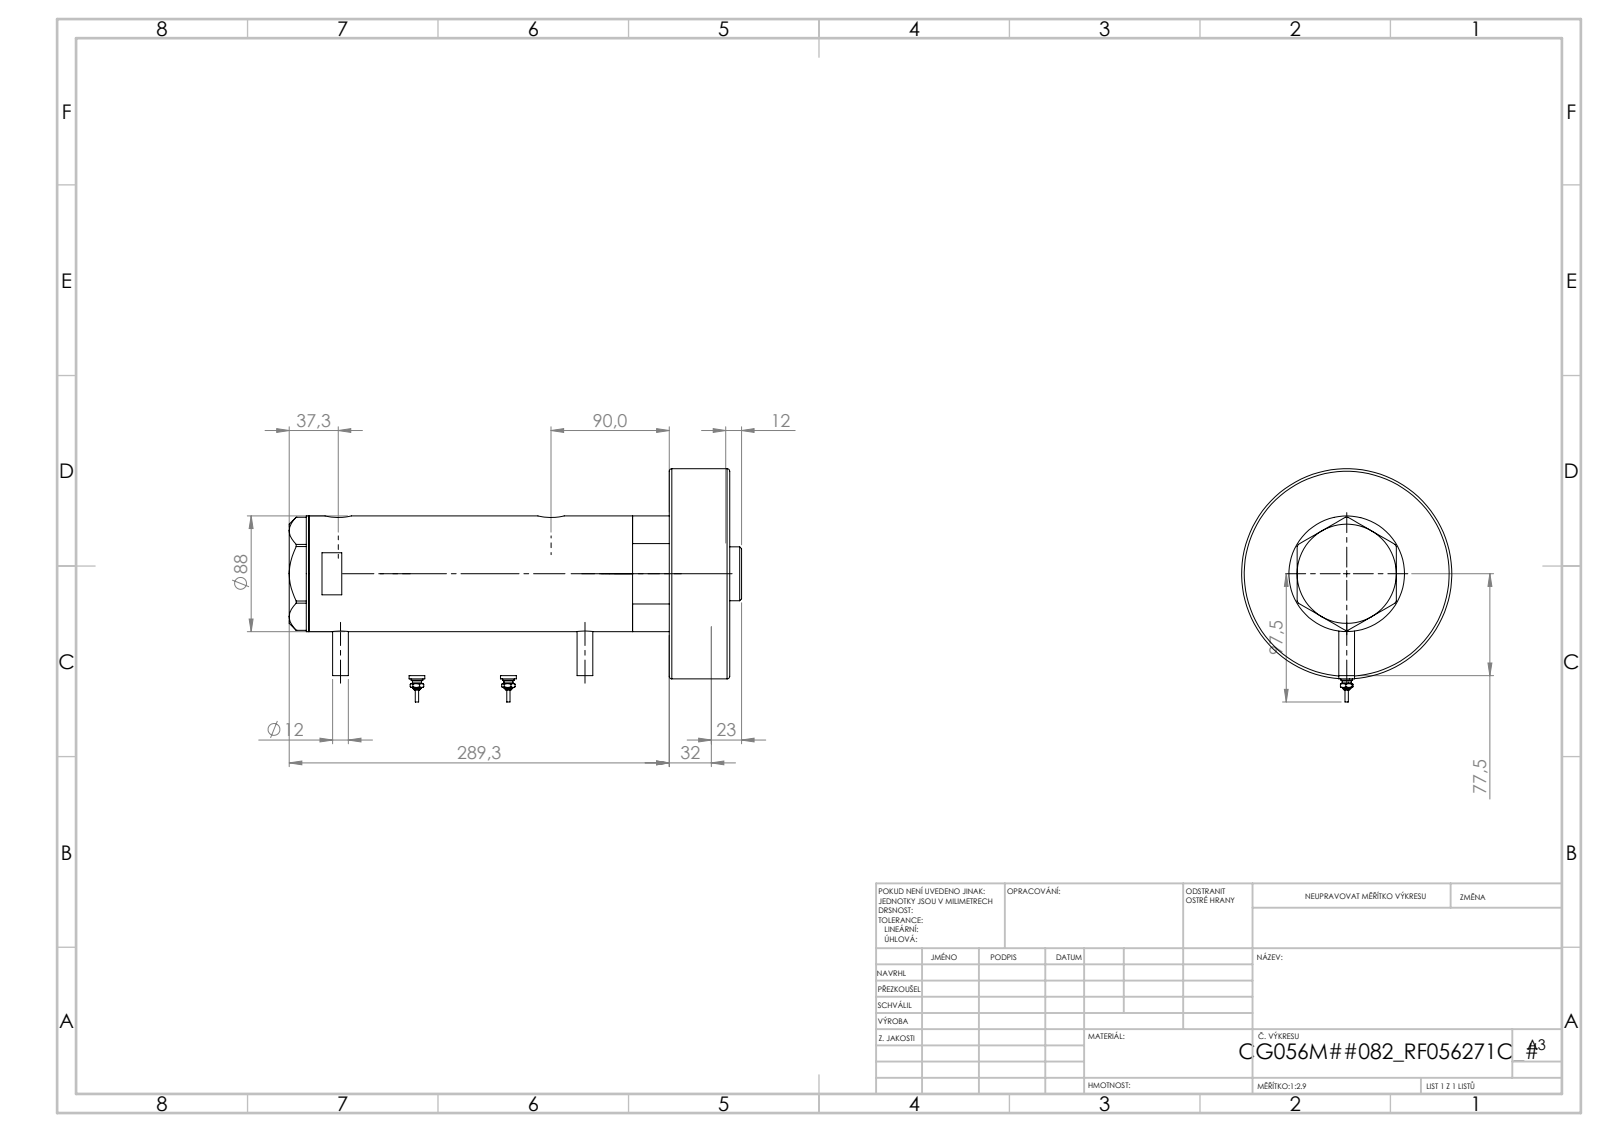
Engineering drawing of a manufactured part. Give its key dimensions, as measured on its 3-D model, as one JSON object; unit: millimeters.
{"part_name": "V270CG_271C; V270CG_BACK; V270CG_SWITCH; V270CG_MIDDLE (+2 more)", "step_written_by": "SolidWorks 2019 (CONFIG_CONTROL_DESIGN)", "units": "millimeters", "bodies": {"solids": 7, "faces": 242, "planar": 83, "cylindrical": 81, "other": 78}, "overall_size": [306.47, 160, 160], "volume_mm3": 2296000, "surface_area_mm2": 294593, "round_holes": [[5, 2], [12.5, 2], [13.16, 2], [20, 2], [14.5, 1], [42, 1], [43.5, 1], [56, 1], [60, 1], [75, 1], [80, 1]], "round_bosses_or_shafts": [[12, 2], [9, 2], [7, 2], [4.34, 2], [2.4, 2], [160, 1], [88, 1], [73, 1]], "face_to_face_distances": [46, 233.9, 279.9, 156.4, 77.5, 123.5, 26, 130.4, 207.9, 253.9], "hole_center_spacings": [1.7, 25.8, 132.3, 134, 158.1, 159.8]}
